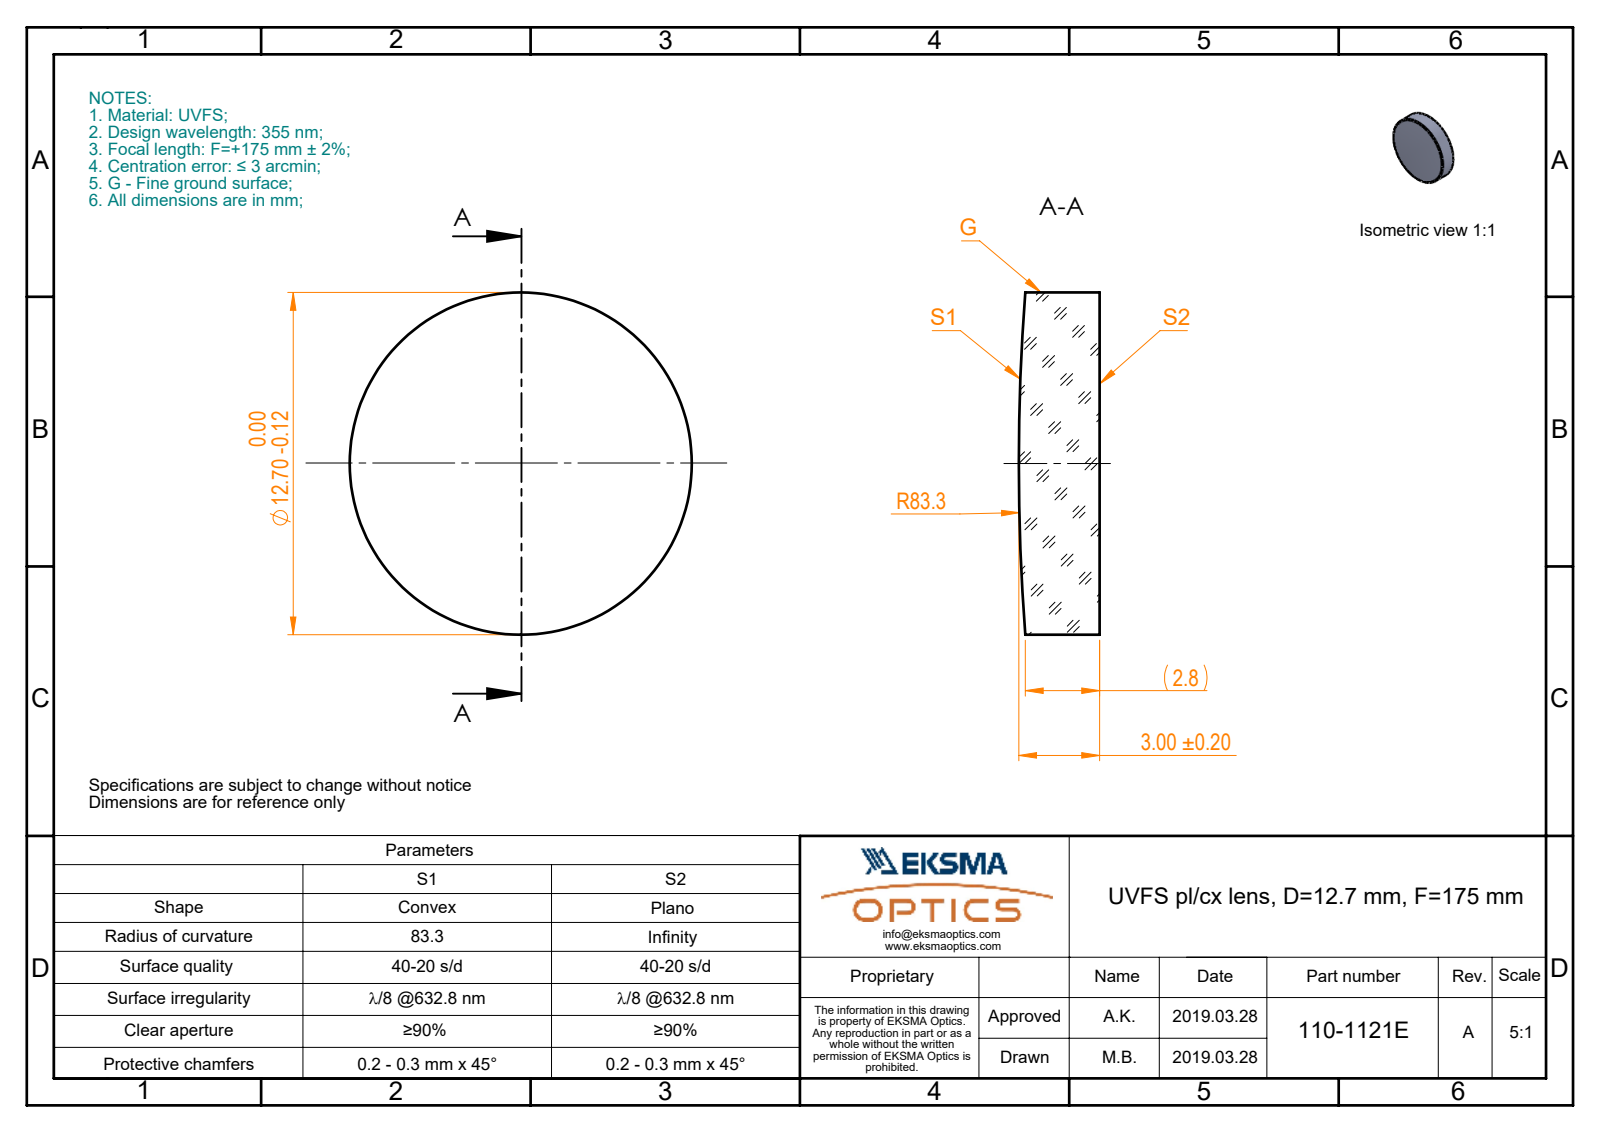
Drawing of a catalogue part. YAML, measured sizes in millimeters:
part_name: "110-1121E UVFS pl-cx 12.7 F175"
step_written_by: "SolidWorks 2017 (CONFIG_CONTROL_DESIGN)"
units: millimeters
bodies: {solids: 1, faces: 5, planar: 1, cylindrical: 2, other: 2}
overall_size: [12.7, 12.7, 3]
volume: 365
surface_area: 364
round_bosses_or_shafts:
  - {diameter: 12.7, count: 1}
